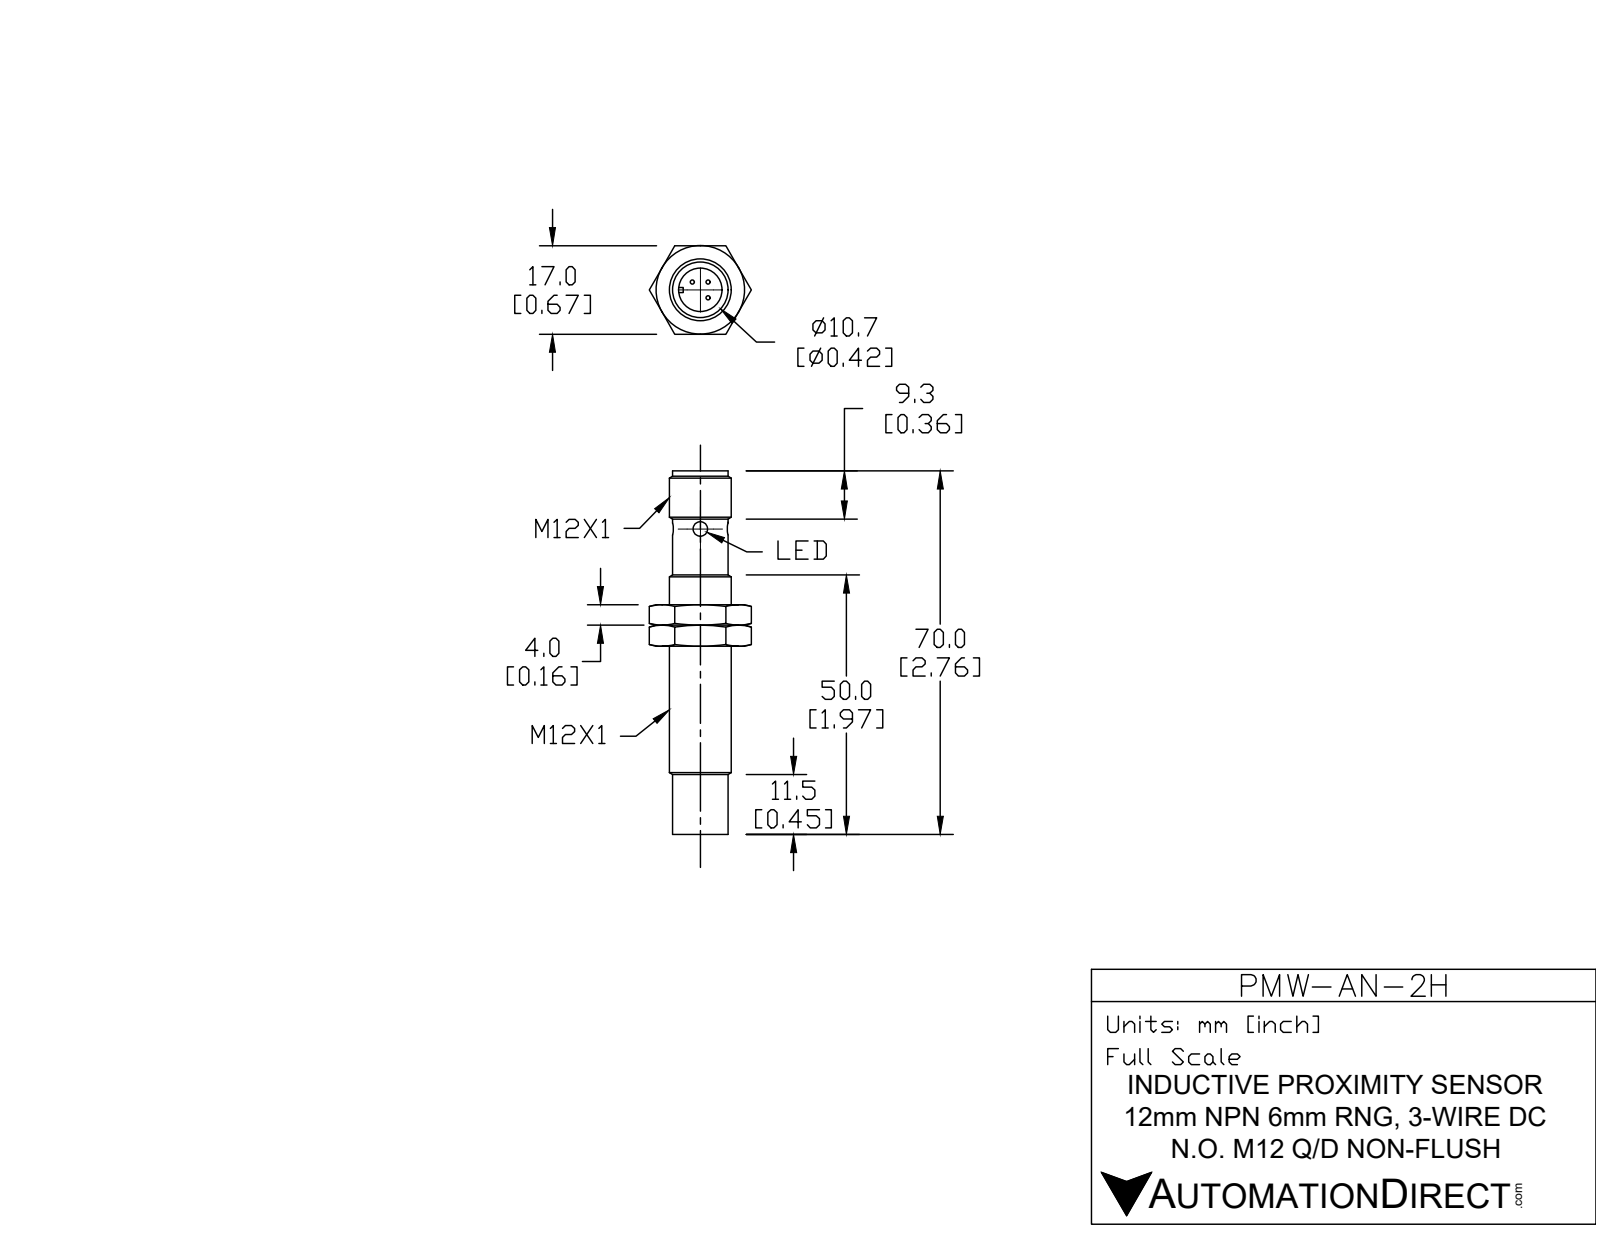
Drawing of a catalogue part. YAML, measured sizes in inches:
part_name: "PMW-AN-2H"
step_written_by: "SolidWorks 2017 (AUTOMOTIVE_DESIGN)"
units: inches
bodies: {solids: 3, faces: 94, planar: 22, cylindrical: 30, other: 42}
overall_size: [2.764, 0.773, 0.669]
volume: 0.5
surface_area: 6.714
round_holes:
  - {diameter: 0.098, count: 2}
  - {diameter: 0.331, count: 1}
  - {diameter: 0.43, count: 1}
round_bosses_or_shafts:
  - {diameter: 0.472, count: 1}
  - {diameter: 0.429, count: 1}
partial_cylinders:
  - {radius: 0.024, count: 1}
  - {radius: 0.197, count: 1}
face_to_face_distances: [0.157, 0.669, 0.315, 1.11, 0.953, 0.795, 1.303, 1.461, 1.618, 2.413]
